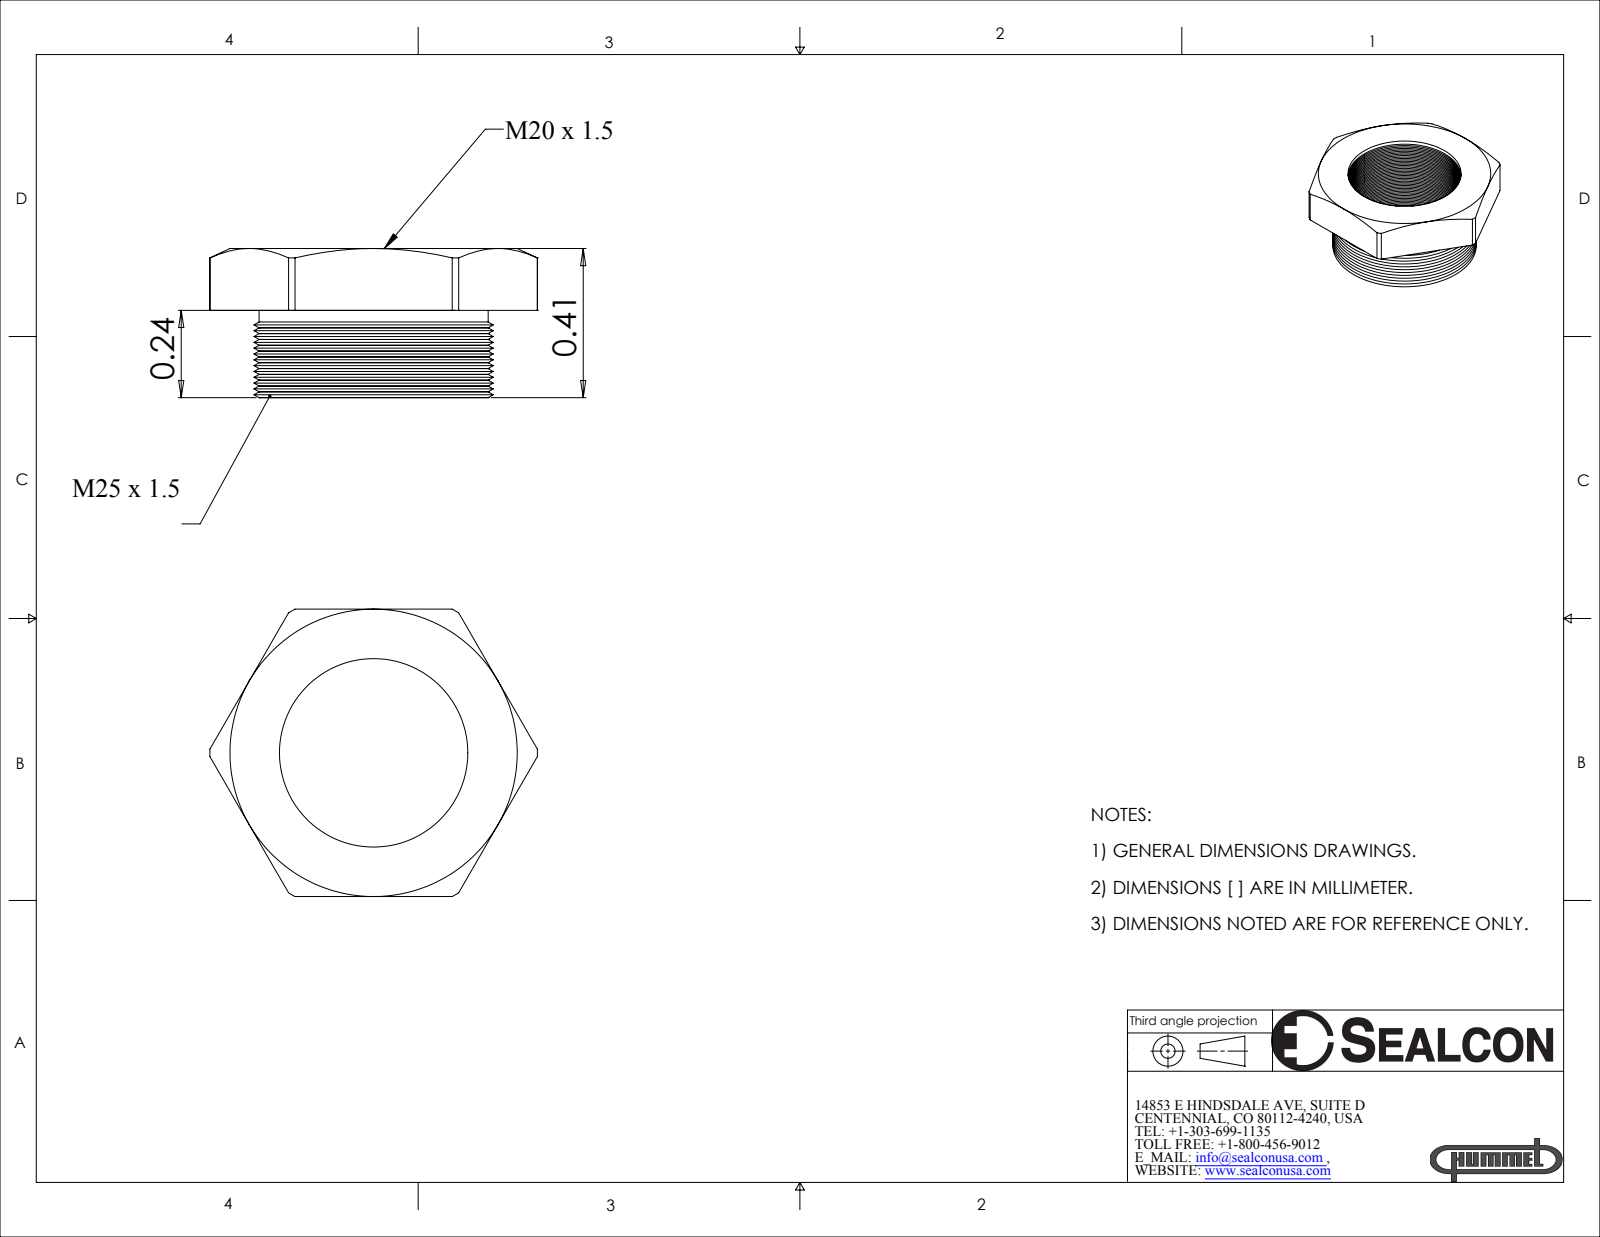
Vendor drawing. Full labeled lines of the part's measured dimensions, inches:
Part name (STEP PRODUCT): RM-2520-SS
STEP written by: SolidWorks 2008 (CONFIG_CONTROL_DESIGN)
Units: inches
Bodies: 1 solid, 255 faces (9 planar, 87 cylindrical, 159 other)
Overall size (bounding box): 0.901 × 0.79 × 0.41
Volume: 0.081 in³ · Surface area: 3.353 in²
Round holes (diameter × count): ⌀0.518 ×1
Round bosses / shafts (diameter × count): ⌀0.63 ×1
Partial cylindrical surfaces — rounded edges, fillets, slot ends (radius × count): R0.45 ×1
Main face-to-face distances: 0.17, 0.79, 0.24, 0.41
